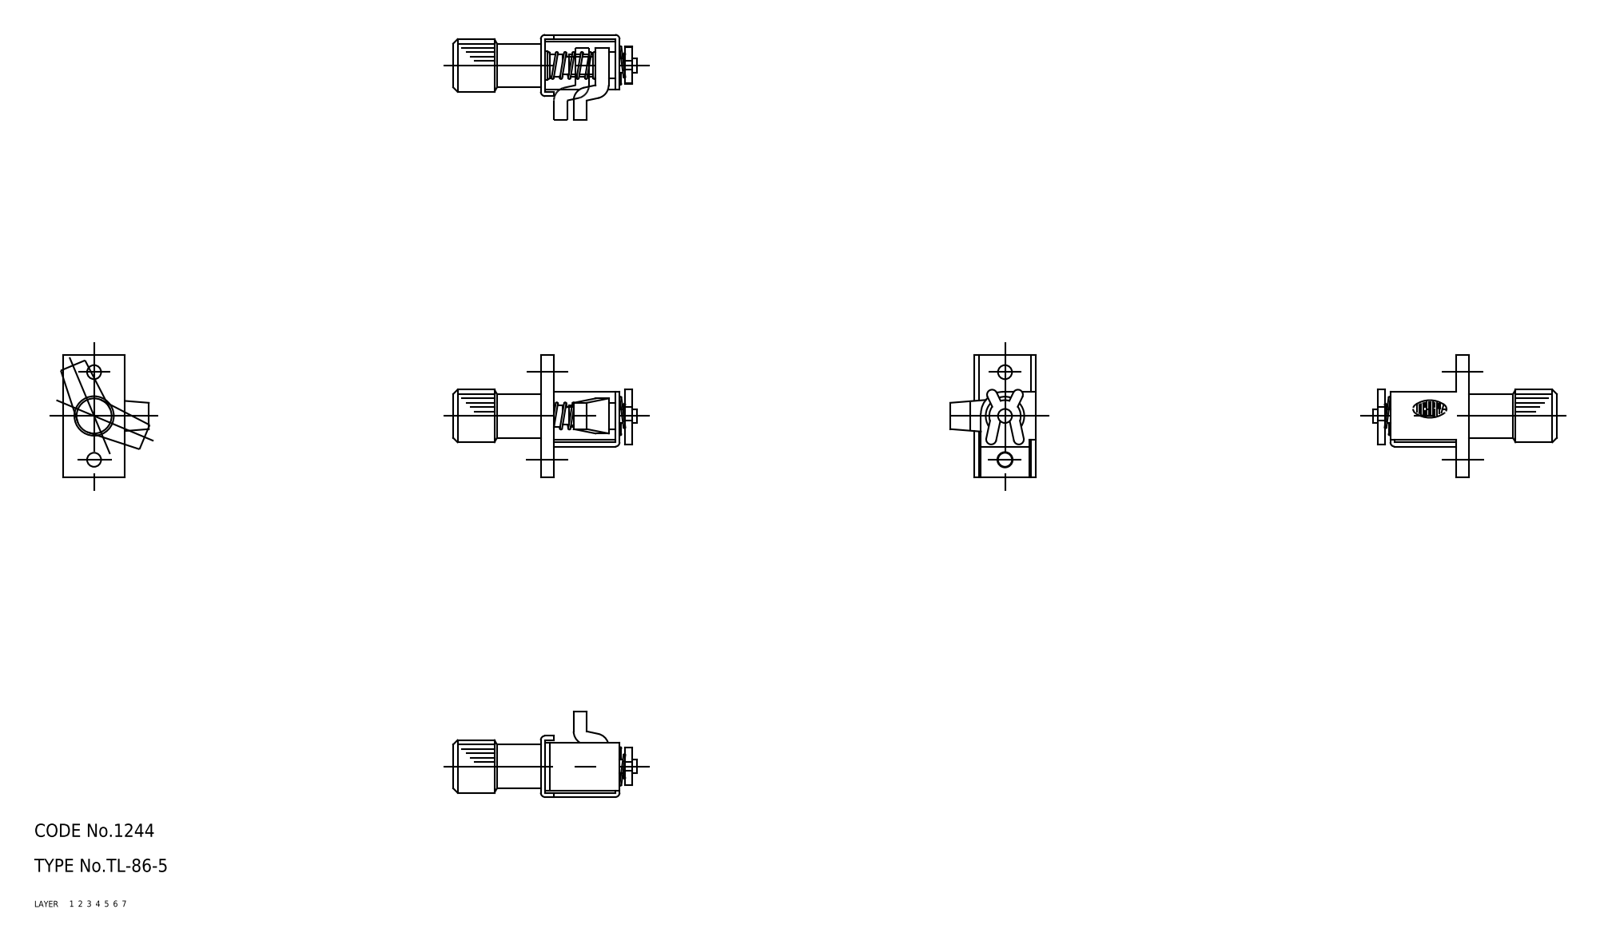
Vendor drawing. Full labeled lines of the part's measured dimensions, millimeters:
Part name (STEP PRODUCT): spring_2; spring_1; retainer; knob (+4 more)
STEP written by: CADfix (AUTOMOTIVE_DESIGN)
Units: millimetres
Bodies: 7 solids, 182 faces (0 planar, 0 cylindrical, 182 other)
Overall size (bounding box): 42 × 28 × 19.5
Volume: 3 728 mm³ · Surface area: 4 421 mm²
